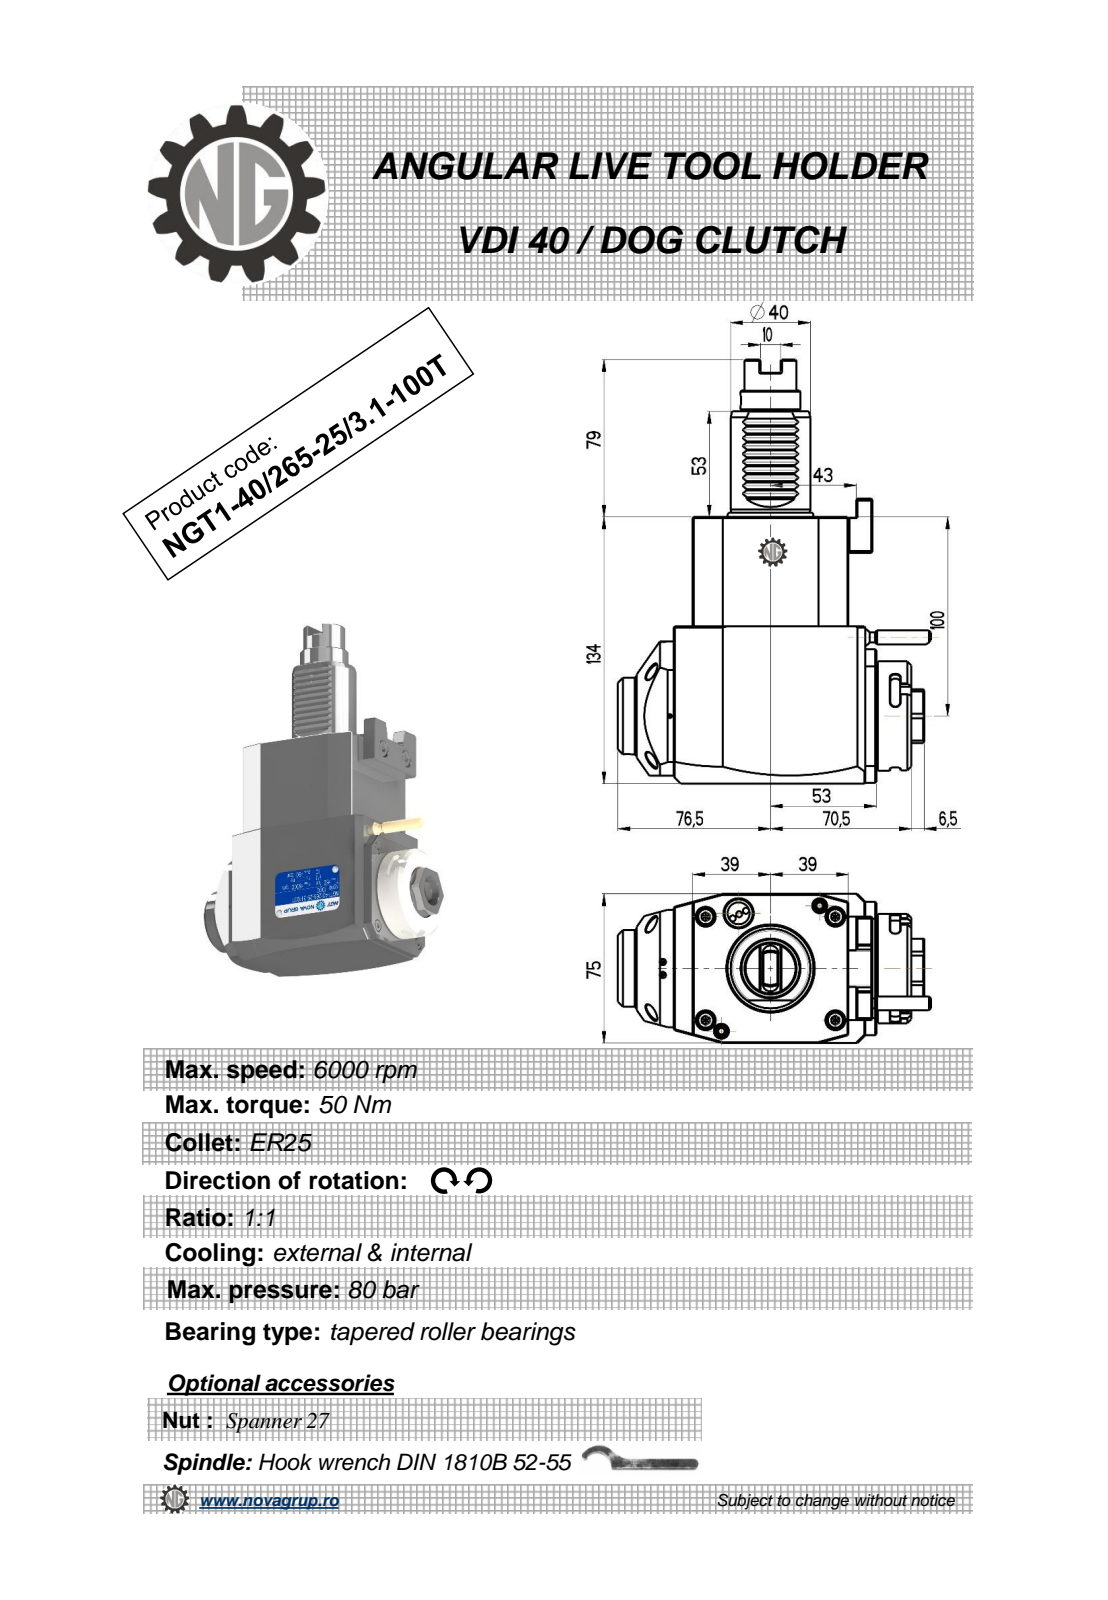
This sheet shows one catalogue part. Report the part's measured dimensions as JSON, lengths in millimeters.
{"part_name": "NGT1_40_265_25_3_1_100T", "step_written_by": "PRO/ENGINEER BY PARAMETRIC TECHNOLOGY CORPORATION, 2010280 (CONFIG_CONTROL_DESIGN)", "units": "millimeters", "bodies": {"solids": 1, "faces": 339, "planar": 204, "cylindrical": 71, "other": 64}, "overall_size": [213, 156.83, 75], "volume_mm3": 1088000, "surface_area_mm2": 77892, "round_holes": [[2.5, 1], [3, 1], [4.2, 1], [18, 1]], "round_bosses_or_shafts": [[55, 1], [48, 1], [40, 1], [38.5, 1], [30, 1], [26, 1], [8, 1], [7, 1]], "partial_cylinders_radius": [[0.3, 10], [0.26, 6], [2.5, 6], [0.5, 3], [1, 2], [180, 2], [12.5, 1], [15, 1]], "face_to_face_distances": [75, 134, 78, 14, 92, 17.5, 31.5, 84.88, 109.5, 4], "hole_center_spacings": [43.2, 120.28, 158.5]}
